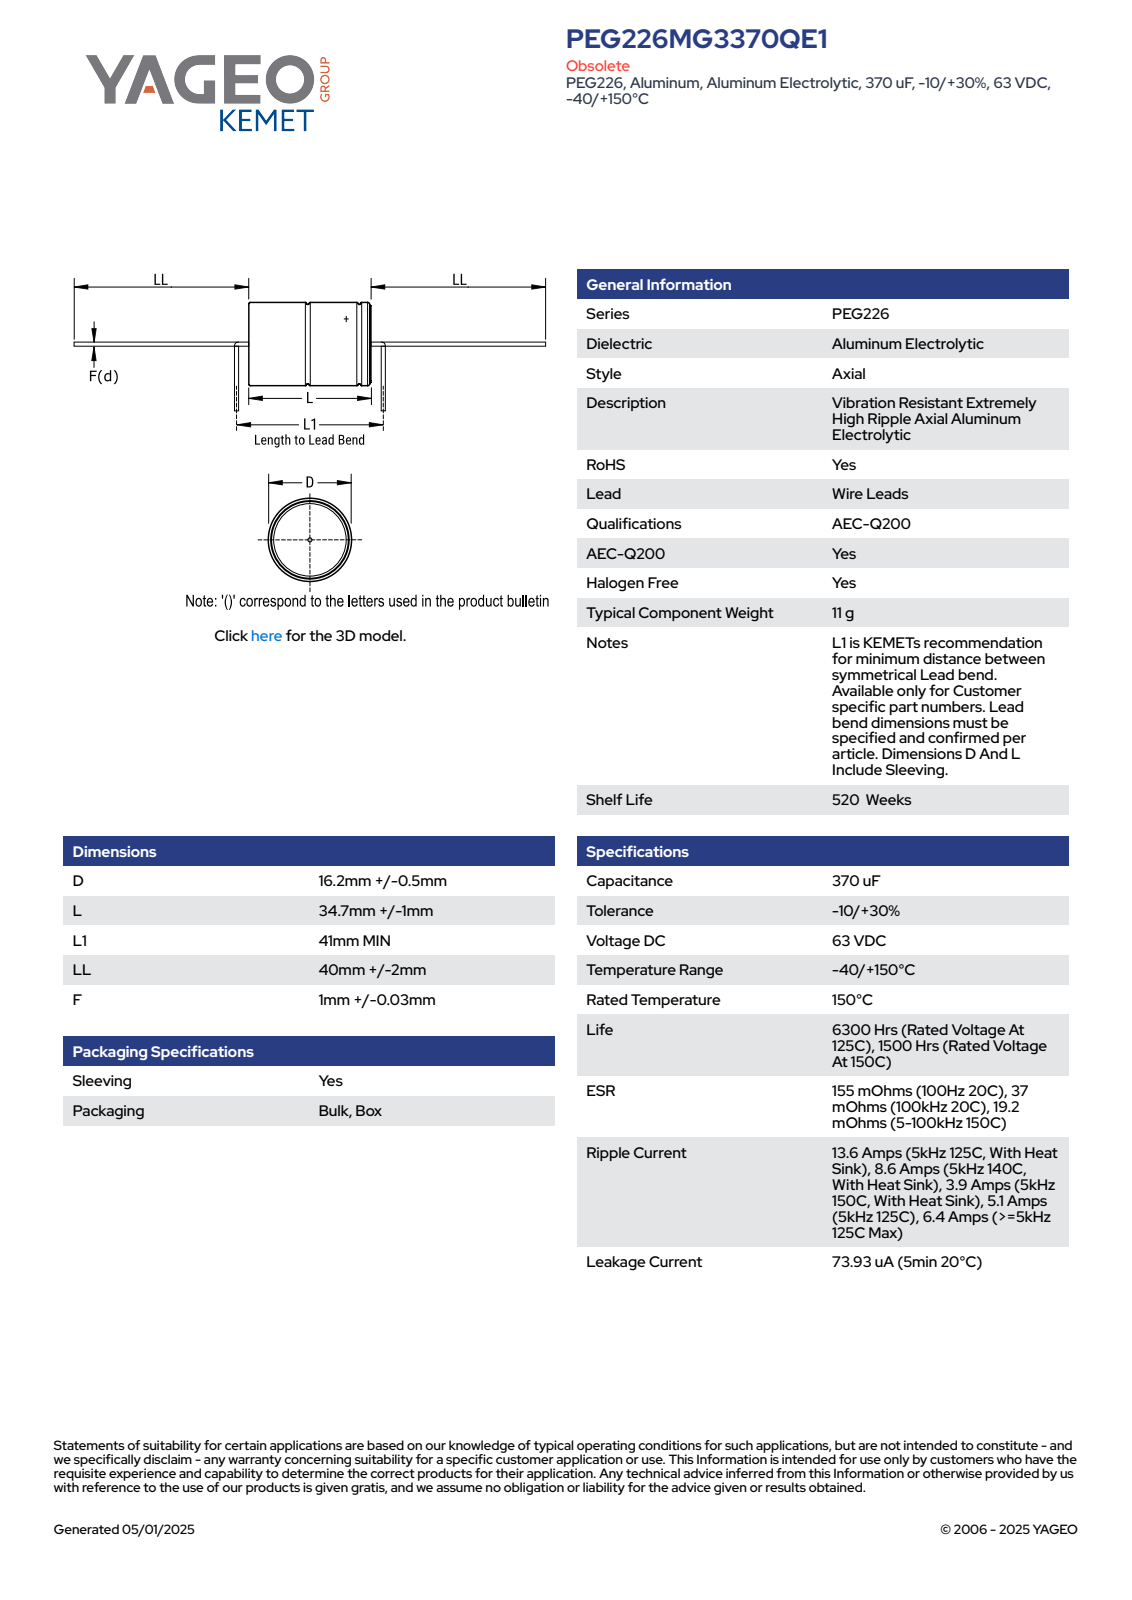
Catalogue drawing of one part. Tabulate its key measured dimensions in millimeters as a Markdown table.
| quantity | value |
| --- | --- |
| part name | CAA_PEG220_16X35_D16.7L35.7LL42F1.03 |
| STEP written by | SolidWorks 2014 (AUTOMOTIVE_DESIGN) |
| units | millimeters |
| bodies | 1 solid, 99 faces (27 planar, 29 cylindrical, 43 other) |
| overall size | 119.7 × 16.7 × 16.7 |
| volume | 7 689 mm³ |
| surface area | 2 639 mm² |
| round holes (diameter × count) | 15.7 × 1 |
| round bosses / shafts (diameter × count) | 16.7 × 1, 16.2 × 1, 1.03 × 1 |
| partial cylindrical surfaces (radius × count) | 8.34 × 1 |
| main face-to-face distances | 34.7, 35.7, 1, 42, 77.7, 76.7, 119.7, 43 |
